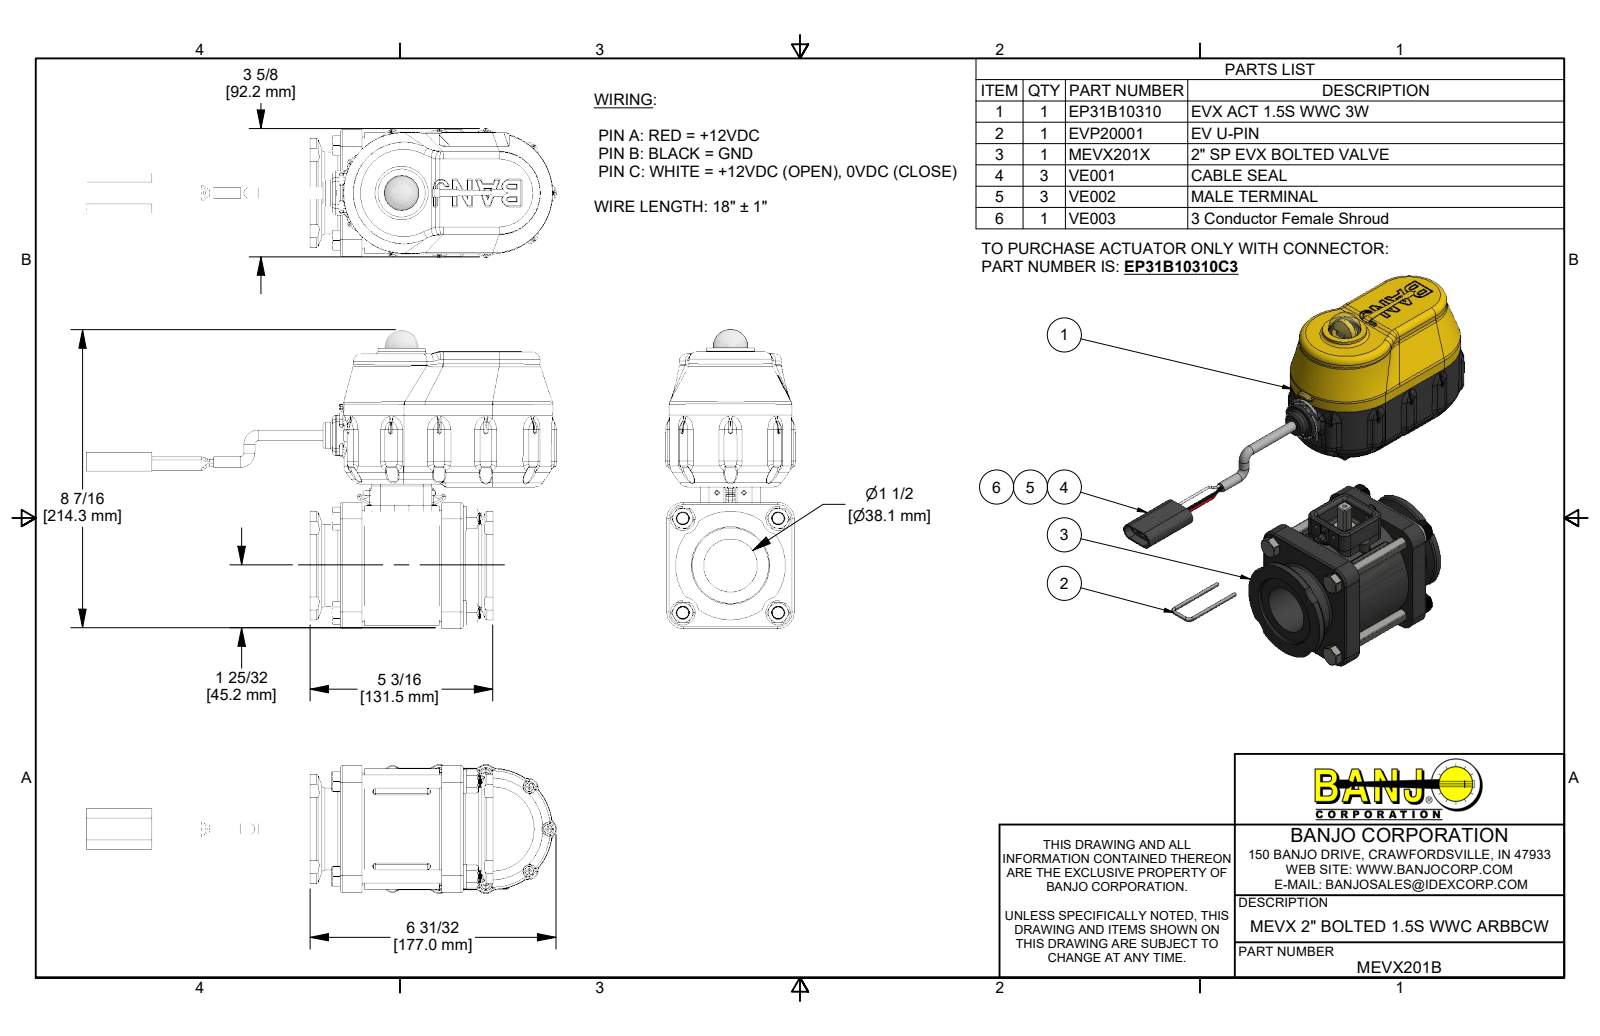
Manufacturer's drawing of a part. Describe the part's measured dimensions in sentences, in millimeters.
The part is named "MEVX201B; EP31B10310; B61905PPHS; B632038PM (+8 more)". Its 3-D file was written by "Autodesk Inventor 2019 (AUTOMOTIVE_DESIGN)". It is 103 solids with 11205 faces: 2866 planar, 3370 cylindrical and 4969 other. Overall it measures 337.6 by 214.3 by 92.2 millimeters. Its volume is 1 064 000 cubic millimeters and its surface area 429 800 square millimeters. Round holes: 11 of diameter 2.4, 11 of diameter 3.8, 7 of diameter 2, 7 of diameter 3.8, 4 of diameter 2.7, 4 of diameter 3.2, 4 of diameter 3.5, 4 of diameter 3.8, 4 of diameter 4.3, 4 of diameter 6.4, 4 of diameter 7.8, 4 of diameter 9.8. Round bosses or shafts: 60 of diameter 8.2, 18 of diameter 2, 17 of diameter 6.4, 11 of diameter 3.6, 11 of diameter 2.7, 11 of diameter 2.2, 6 of diameter 1.5, 5 of diameter 9.5. Partial cylindrical surfaces (rounded edges, fillets, slot ends): 180 of radius 0.3, 145 of radius 1, 84 of radius 0.3, 78 of radius 0.5, 53 of radius 0.1, 36 of radius 1.5, 30 of radius 0.8, 28 of radius 2. The main face-to-face distances are 2.5, 1.5, 42.8, 65.2, 15.5, 72.8, 18.5, 5.4, 3.8, 3.2. The hole center spacings are 47.8, 67.5, 68.3, 69, 42.2, 45.1, 53, 69.3.
